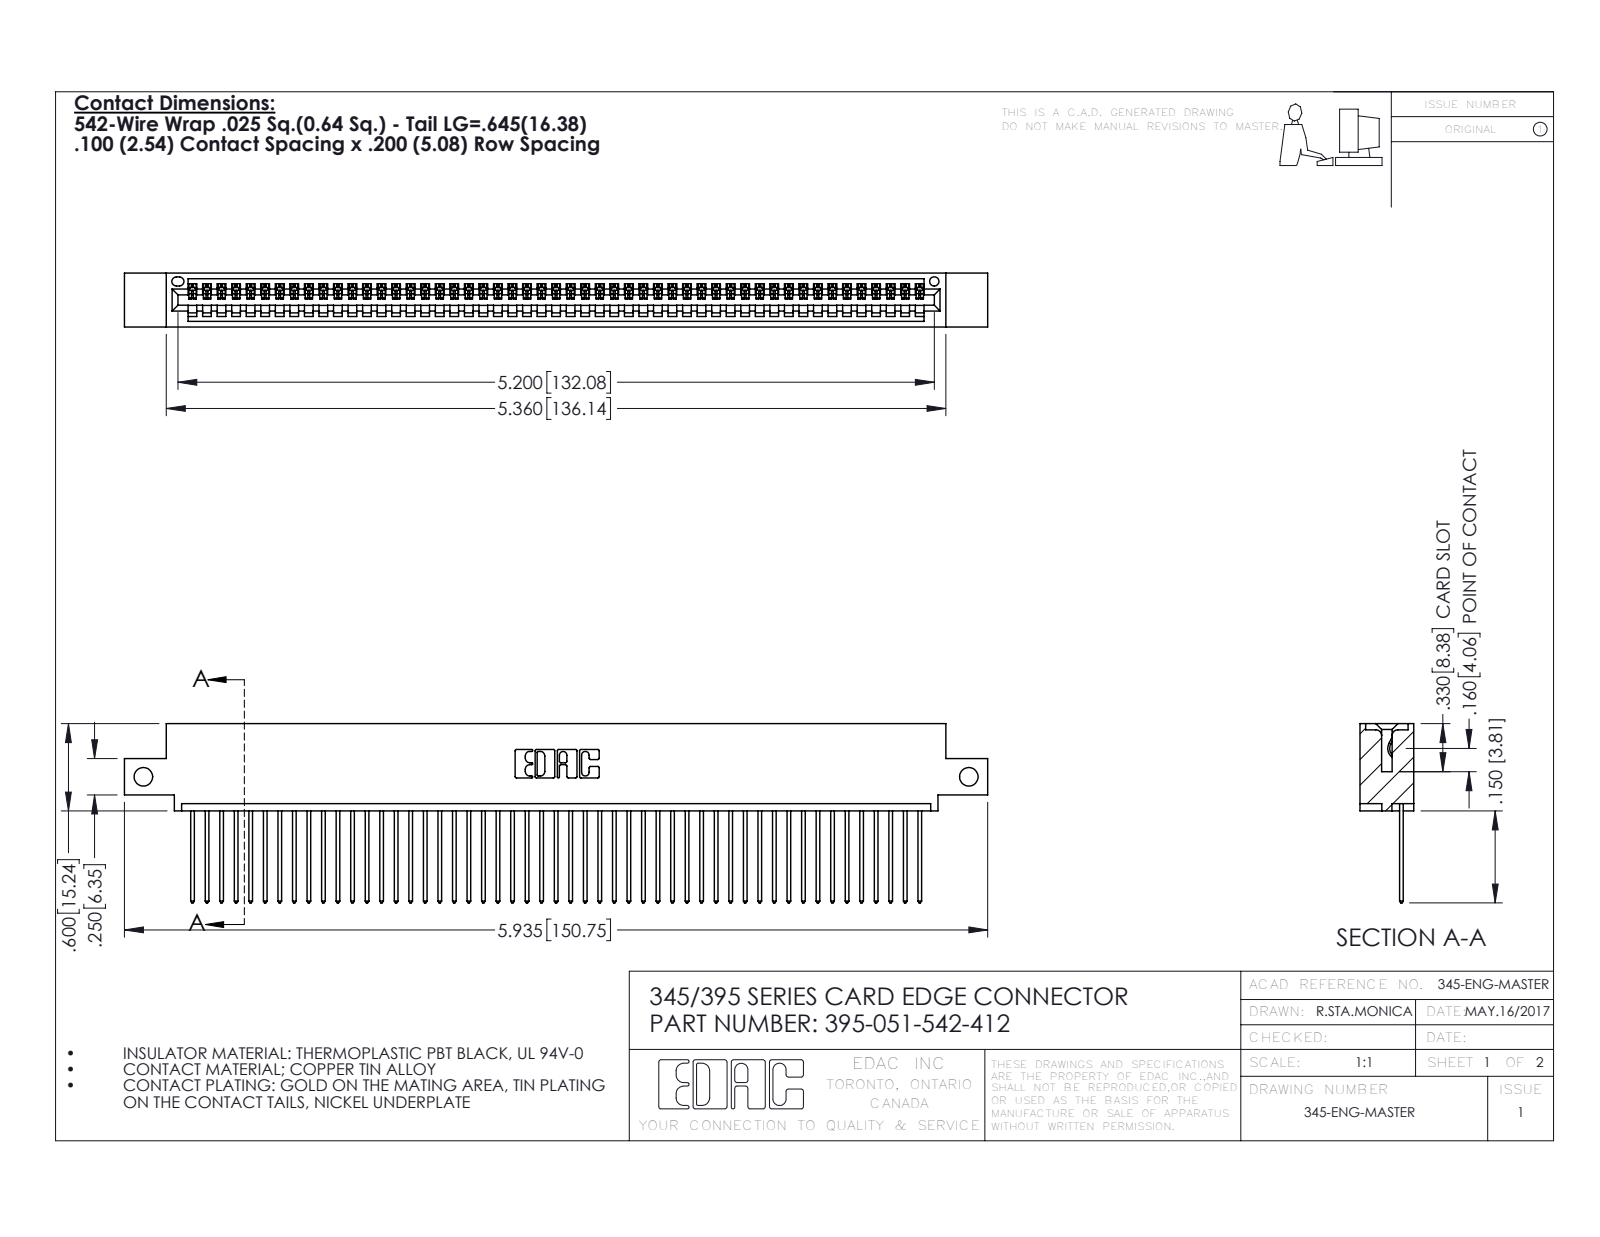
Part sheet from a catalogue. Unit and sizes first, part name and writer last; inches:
Units: inches
Overall size (bounding box): 5.935 × 1.232 × 0.37
Round holes (diameter × count): ⌀0.128 ×2, ⌀0.064 ×1
Partial cylindrical surfaces — rounded edges, fillets, slot ends (radius × count): R0.006 ×102, R0.01 ×102, R0.01 ×22, R0.007 ×6, R0.031 ×6, R0.026 ×3, R0.031 ×2, R0.04 ×2
Main face-to-face distances: 0.072, 0.298, 0.098, 0.272, 0.025, 0.37, 0.2, 0.225, 0.149, 0.072
Hole centre spacings: 5.675
Volume: 0.875 in³ · Surface area: 30.76 in²
Bodies: 52 solids, 3088 faces (2124 planar, 964 cylindrical, 0 other)
Part name (STEP PRODUCT): 345-292-001_345-293-142; 345 Part_0.110 Offset - Side Mount; 395-051-542-412
STEP written by: SolidWorks 2016 (CONFIG_CONTROL_DESIGN)
